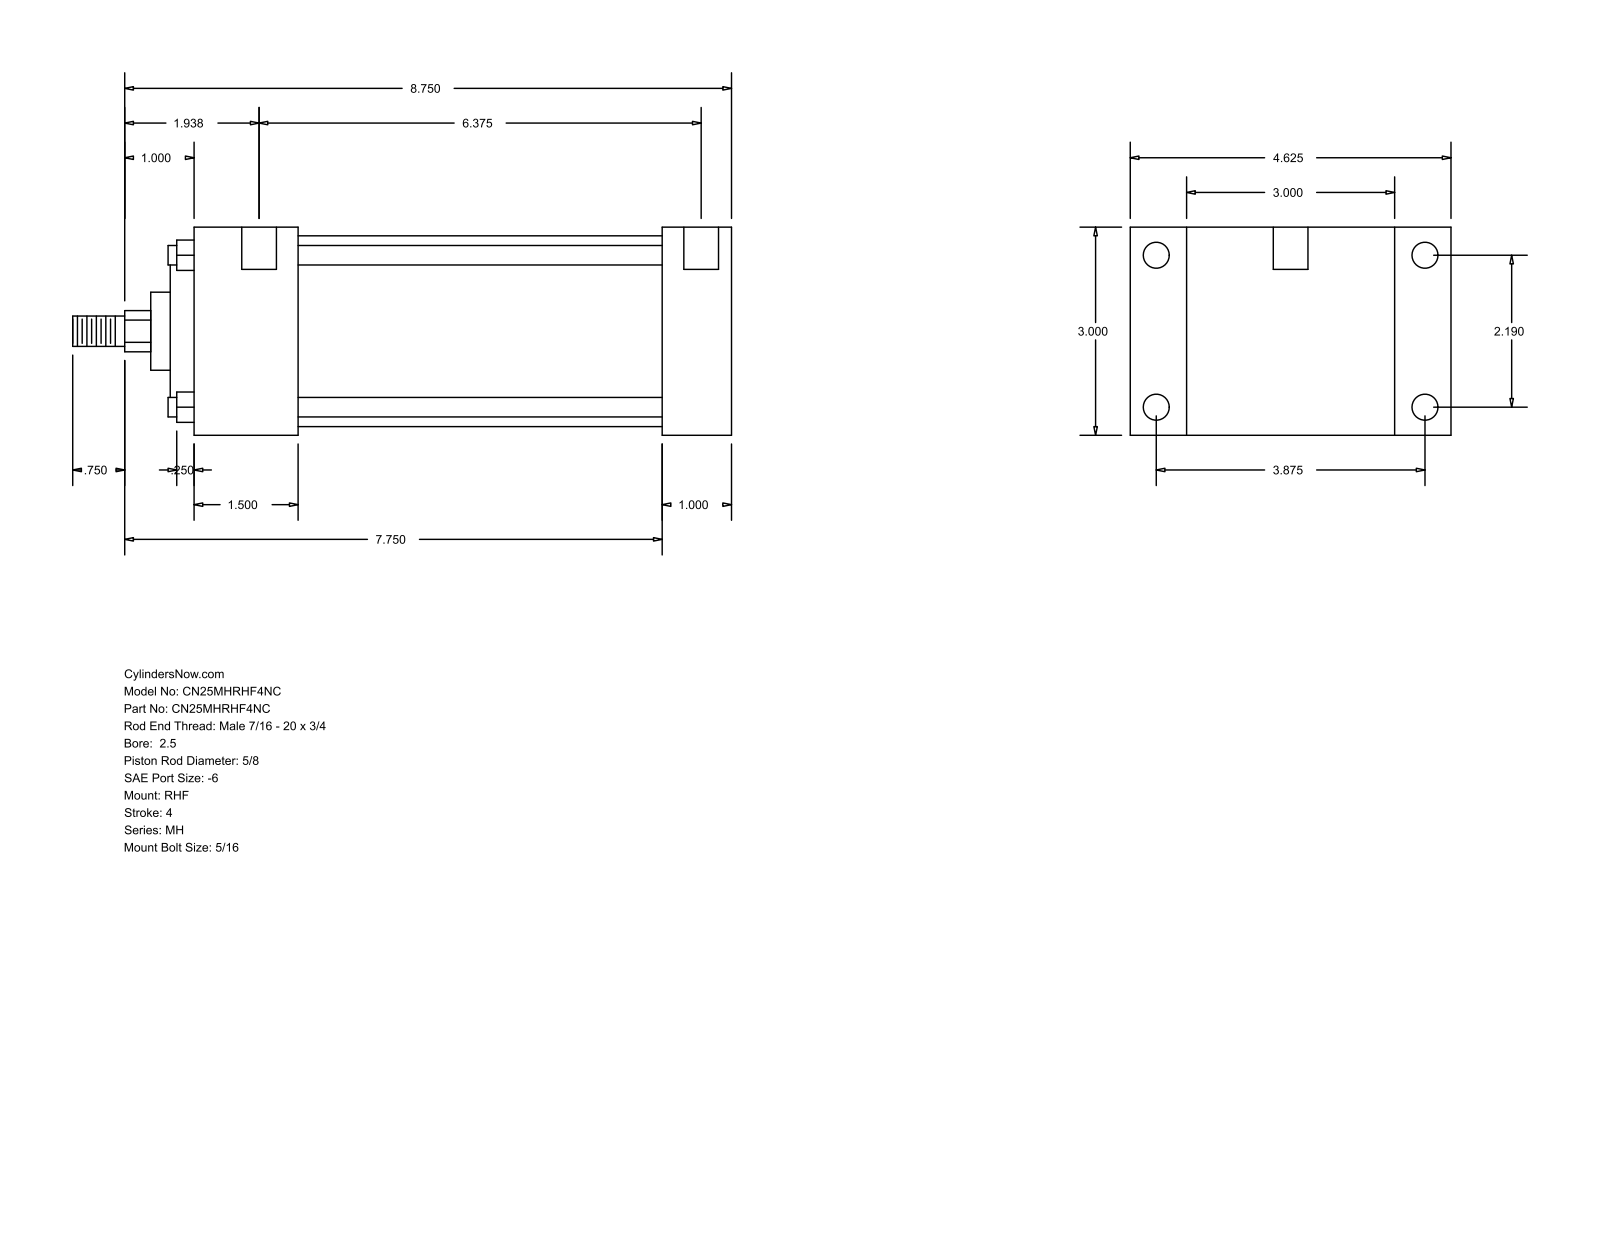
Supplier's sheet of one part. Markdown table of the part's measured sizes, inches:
| quantity | value |
| --- | --- |
| part name | MH_RHF__0250_0.625 |
| STEP written by | GSSL Pune (CONFIG_CONTROL_DESIGN) |
| units | inches |
| bodies | 0 solids, 90 faces (61 planar, 29 cylindrical, 0 other) |
| overall size | 9.5 × 4.625 × 3 |
| round holes (diameter × count) | 0.219 × 4, 0.375 × 4, 0.5 × 2 |
| round bosses / shafts (diameter × count) | 0.281 × 4, 2.75 × 1, 2.187 × 1, 1.125 × 1, 0.625 × 1, 0.437 × 1 |
| partial cylindrical surfaces (radius × count) | 0.297 × 1 |
| main face-to-face distances | 3, 1, 0.813, 3.813, 7.75, 6.75, 1.5, 4.625, 5.25, 6.25 |
| hole center spacings | 2.19, 3.875, 4.451, 6.687, 0.125, 0.187, 6.375, 6.5 |
